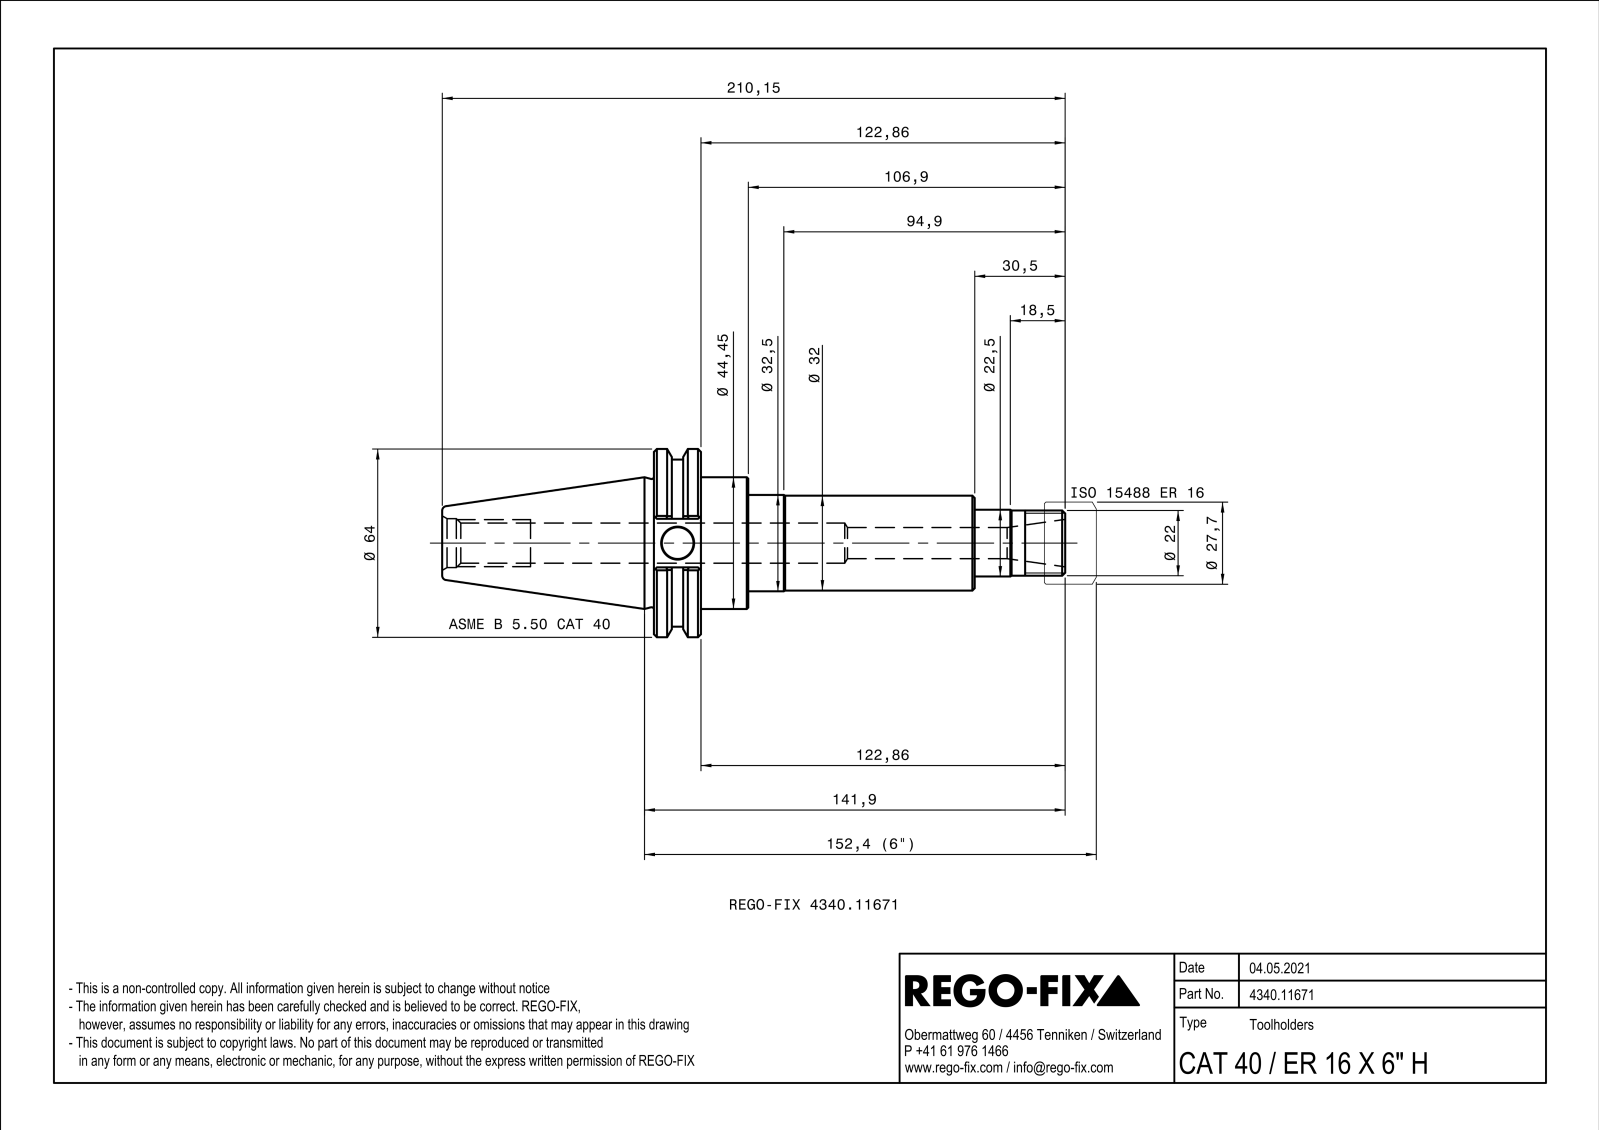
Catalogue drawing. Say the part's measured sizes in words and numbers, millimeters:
The part is named "NOCUT". Its 3-D file was written by "SIEMENS PLM Software Solid Edge ST10 (AUTOMOTIVE_DESIGN)". It is 1 solid with 115 faces: 32 planar, 26 cylindrical and 57 other. Overall it measures 210.15 by 63.5 by 60.79 millimeters. Its volume is 183 270 cubic millimeters and its surface area 36 803 square millimeters. Round holes: 1 of diameter 10.5, 1 of diameter 10.7, 1 of diameter 13.53, 1 of diameter 16.5. Round bosses or shafts: 1 of diameter 63.5, 1 of diameter 56.36, 1 of diameter 44.45, 1 of diameter 32.5, 1 of diameter 32, 1 of diameter 22.5, 1 of diameter 22. Partial cylindrical surfaces (rounded edges, fillets, slot ends): 4 of radius 0.5. The main face-to-face distances are 15.87, 15.96, 31.83, 76.4, 92.36, 108.23, 47.33, 16.38, 179.65, 103.25.
